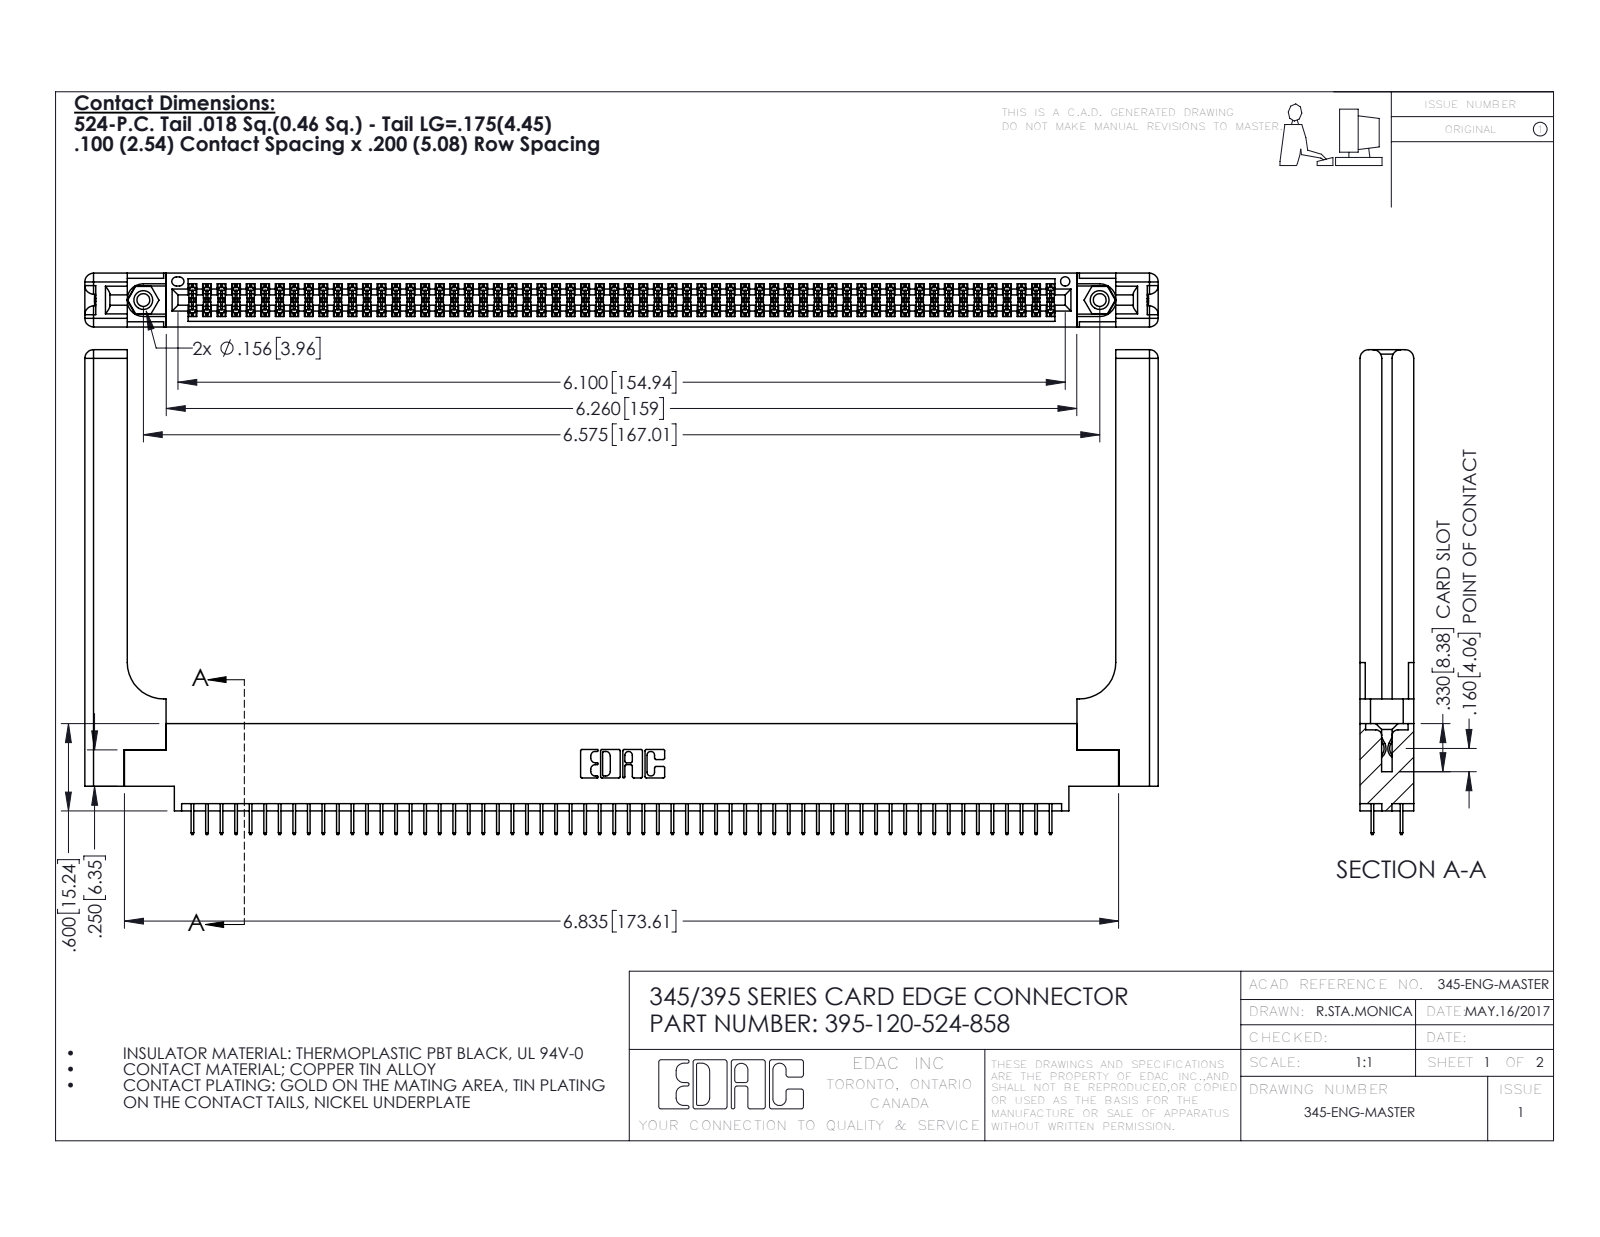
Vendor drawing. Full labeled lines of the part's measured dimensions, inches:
Part name (STEP PRODUCT): 345-250-001_345-250-001-102; 345-220-058_345-220-058; 395-120-524-858; 345 Part_0.170 Offset - 0.156 Dia-TH (+1 more)
STEP written by: SolidWorks 2016 (CONFIG_CONTROL_DESIGN)
Units: inches
Bodies: 125 solids, 6866 faces (4912 planar, 1894 cylindrical, 60 other)
Overall size (bounding box): 7.379 × 3.332 × 0.37
Volume: 1.62 in³ · Surface area: 49.28 in²
Round holes (diameter × count): ⌀0.089 ×2, ⌀0.125 ×2, ⌀0.156 ×2, ⌀0.064 ×1
Round bosses / shafts (diameter × count): ⌀0.155 ×2
Partial cylindrical surfaces — rounded edges, fillets, slot ends (radius × count): R0.006 ×180, R0.01 ×22, R0.06 ×16, R0.007 ×6, R0.031 ×6, R0.026 ×3, R0.014 ×2, R0.019 ×2
Main face-to-face distances: 0.072, 0.37, 0.298, 0.2, 0.098, 0.272, 0.025, 0.225, 0.175, 0.072
Hole centre spacings: 0.27, 6.339, 6.575
